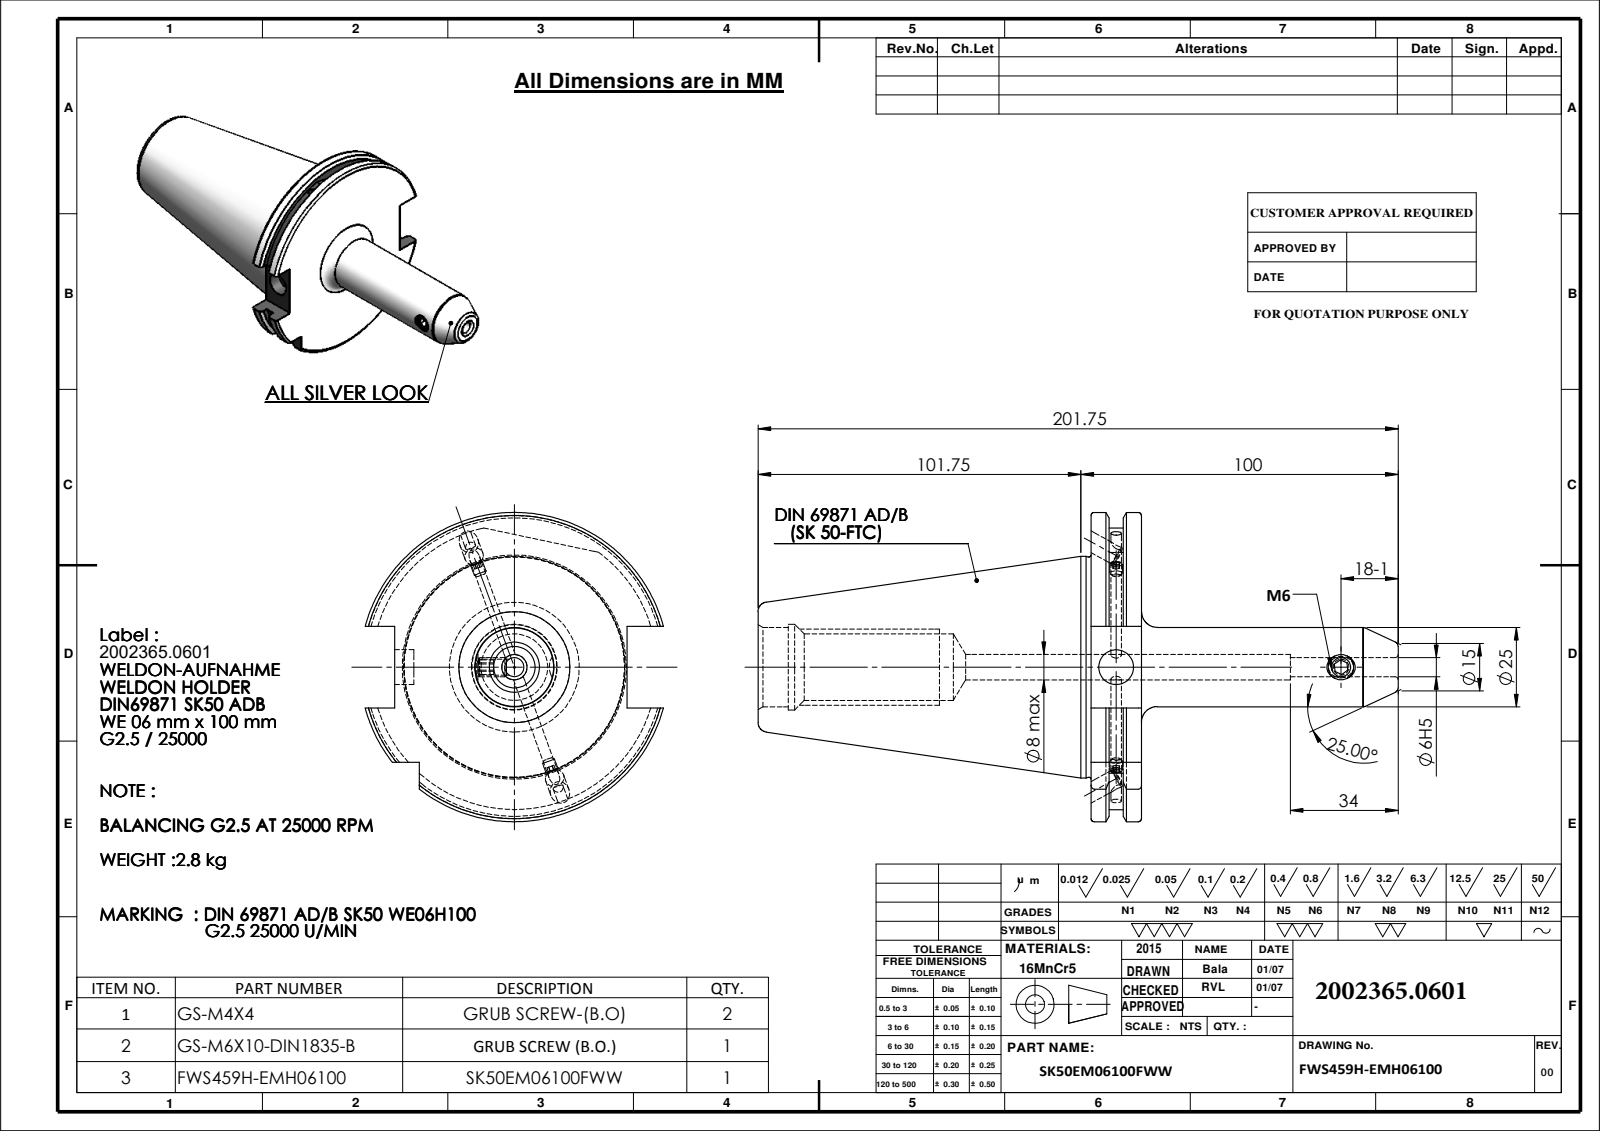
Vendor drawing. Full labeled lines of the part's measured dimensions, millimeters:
Part name (STEP PRODUCT): M6X10._DIN 913 - M8 x 8-N; 91506-WE706100; SK50 EM 06 100 FTC WW.; Copy of M4X4_DIN 913 - M4 x 4-N
STEP written by: SolidWorks 2009 (CONFIG_CONTROL_DESIGN)
Units: millimetres
Bodies: 4 solids, 164 faces (51 planar, 53 cylindrical, 60 other)
Overall size (bounding box): 201.75 × 97.5 × 94.05
Volume: 369 699 mm³ · Surface area: 51 258 mm²
Round holes (diameter × count): ⌀6 ×3, ⌀8 ×2, ⌀3.3 ×1, ⌀5 ×1, ⌀11 ×1, ⌀21 ×1, ⌀25 ×1, ⌀27 ×1
Round bosses / shafts (diameter × count): ⌀4 ×2, ⌀69.85 ×1, ⌀69.45 ×1, ⌀6 ×1
Partial cylindrical surfaces — rounded edges, fillets, slot ends (radius × count): R44.9 ×1, R48.75 ×1
Main face-to-face distances: 15.9, 5.66, 10.24, 10.15, 4.49, 5.75, 104.95, 110.61, 115.1, 120.85
Hole centre spacings: 70.9
